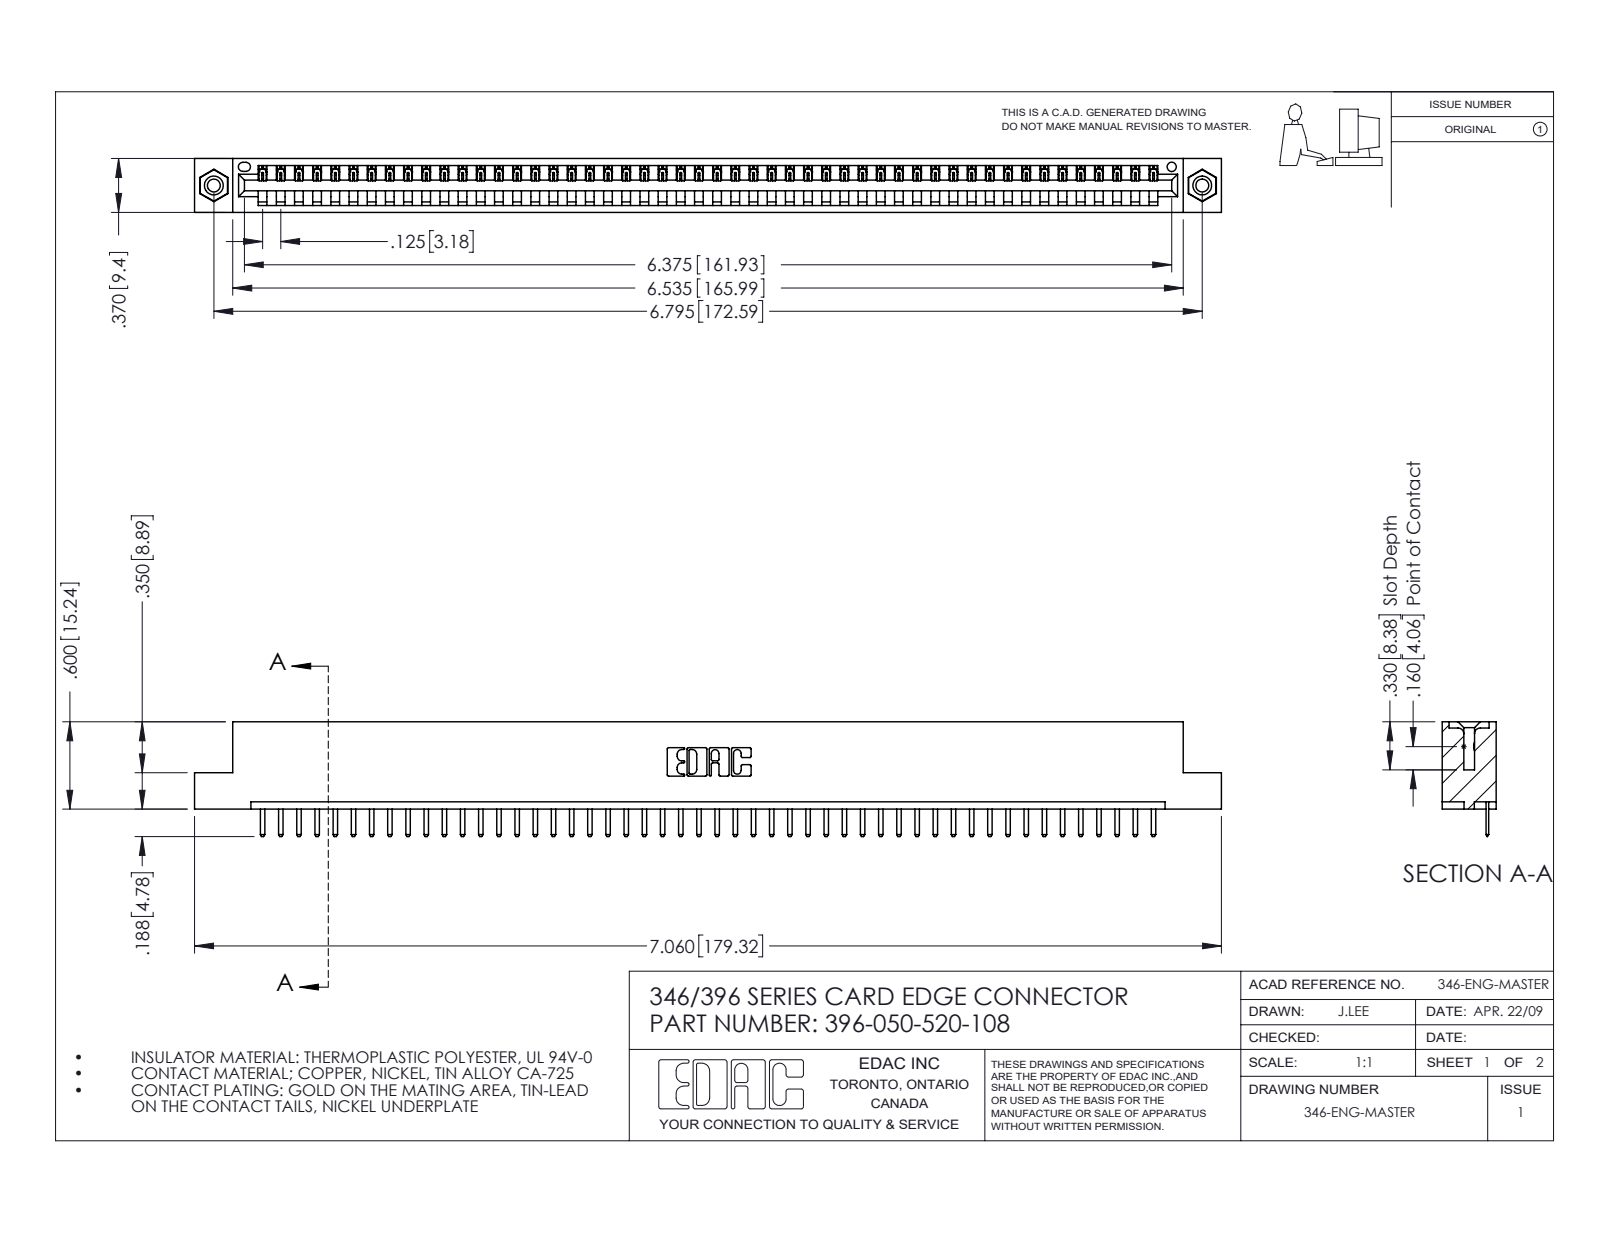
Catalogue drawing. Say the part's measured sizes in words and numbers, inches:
The part is named "345-292-001_345-293-120; 345-250-001_345-250-003-102; 346 Part_Flush Mounting Lugs - 0.156 Dia-TI; 396-050-520-108". Its 3-D file was written by "SolidWorks 2016 (CONFIG_CONTROL_DESIGN)". It is 53 solids with 3282 faces: 2208 planar, 1058 cylindrical and 16 other. Overall it measures 7.06 by 0.788 by 0.37 inches. Its volume is 1.042 cubic inches and its surface area 32.49 square inches. Round holes: 2 of diameter 0.089, 2 of diameter 0.125, 2 of diameter 0.156, 1 of diameter 0.064. Round bosses or shafts: 2 of diameter 0.155. Partial cylindrical surfaces (rounded edges, fillets, slot ends): 102 of radius 0.01, 100 of radius 0.006, 22 of radius 0.01, 6 of radius 0.007, 6 of radius 0.031, 3 of radius 0.026, 2 of radius 0.031, 2 of radius 0.04. The main face-to-face distances are 0.048, 0.322, 0.37, 0.25, 0.148, 0.222, 0.1, 0.174, 0.072, 0.298. The hole center spacings are 0.246, 6.586, 6.795.
